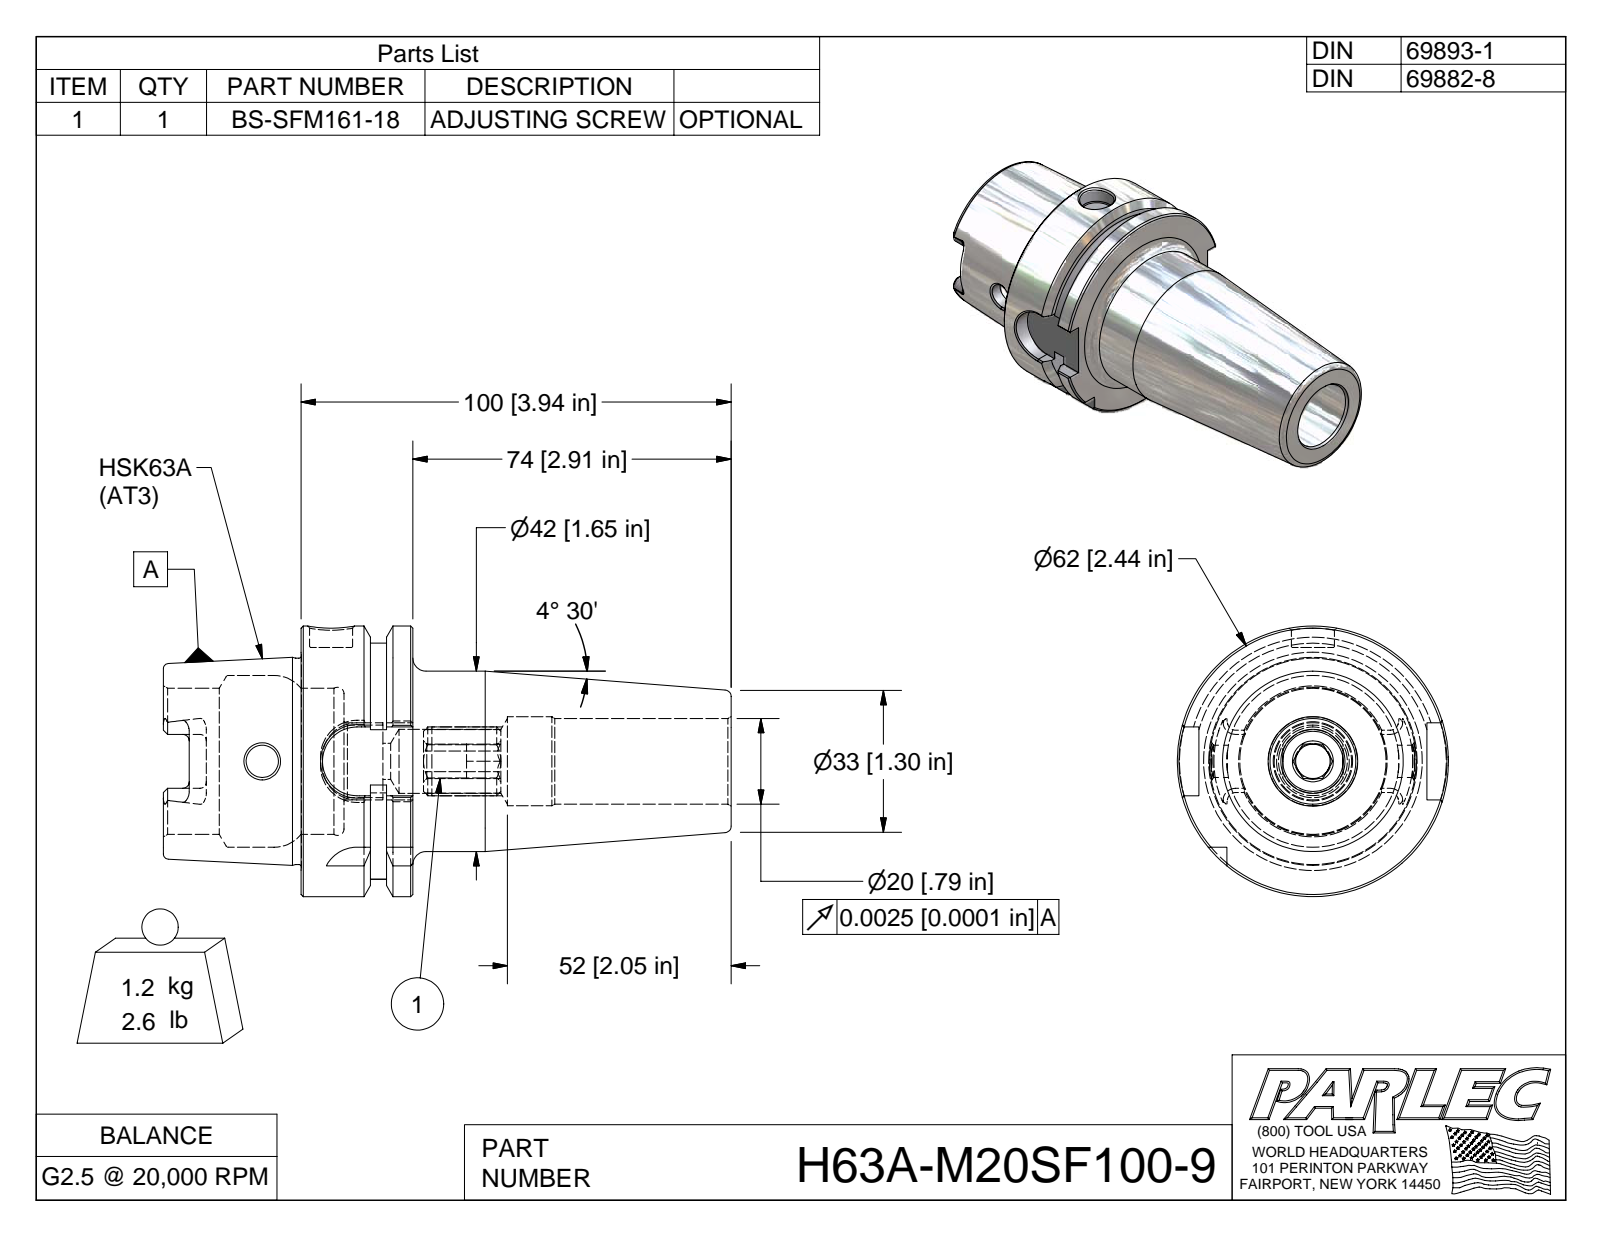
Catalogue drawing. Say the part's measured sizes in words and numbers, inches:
The part is named "H63A-M20SF100-9; H63A-M20SF100-9-1; BS-SFM161-18". Its 3-D file was written by "Autodesk Inventor 2009 (AUTOMOTIVE_DESIGN)". It is 2 solids with 157 faces: 58 planar, 35 cylindrical and 64 other. Overall it measures 5.197 by 2.48 by 2.48 inches. Its volume is 9.161 cubic inches and its surface area 56.44 square inches. Round holes: 1 of diameter 0.295, 1 of diameter 0.394, 1 of diameter 0.666, 1 of diameter 0.786, 1 of diameter 0.816, 1 of diameter 1.339, 1 of diameter 1.575. Round bosses or shafts: 1 of diameter 2.48, 1 of diameter 1.891, 1 of diameter 1.654. Partial cylindrical surfaces (rounded edges, fillets, slot ends): 6 of radius 0.059, 5 of radius 0.315, 4 of radius 0.113, 1 of radius 1.083. The main face-to-face distances are 1.024, 0.241, 0.389, 0.394, 0.63, 1.26, 2.913, 3.937, 3.543, 1.654.
